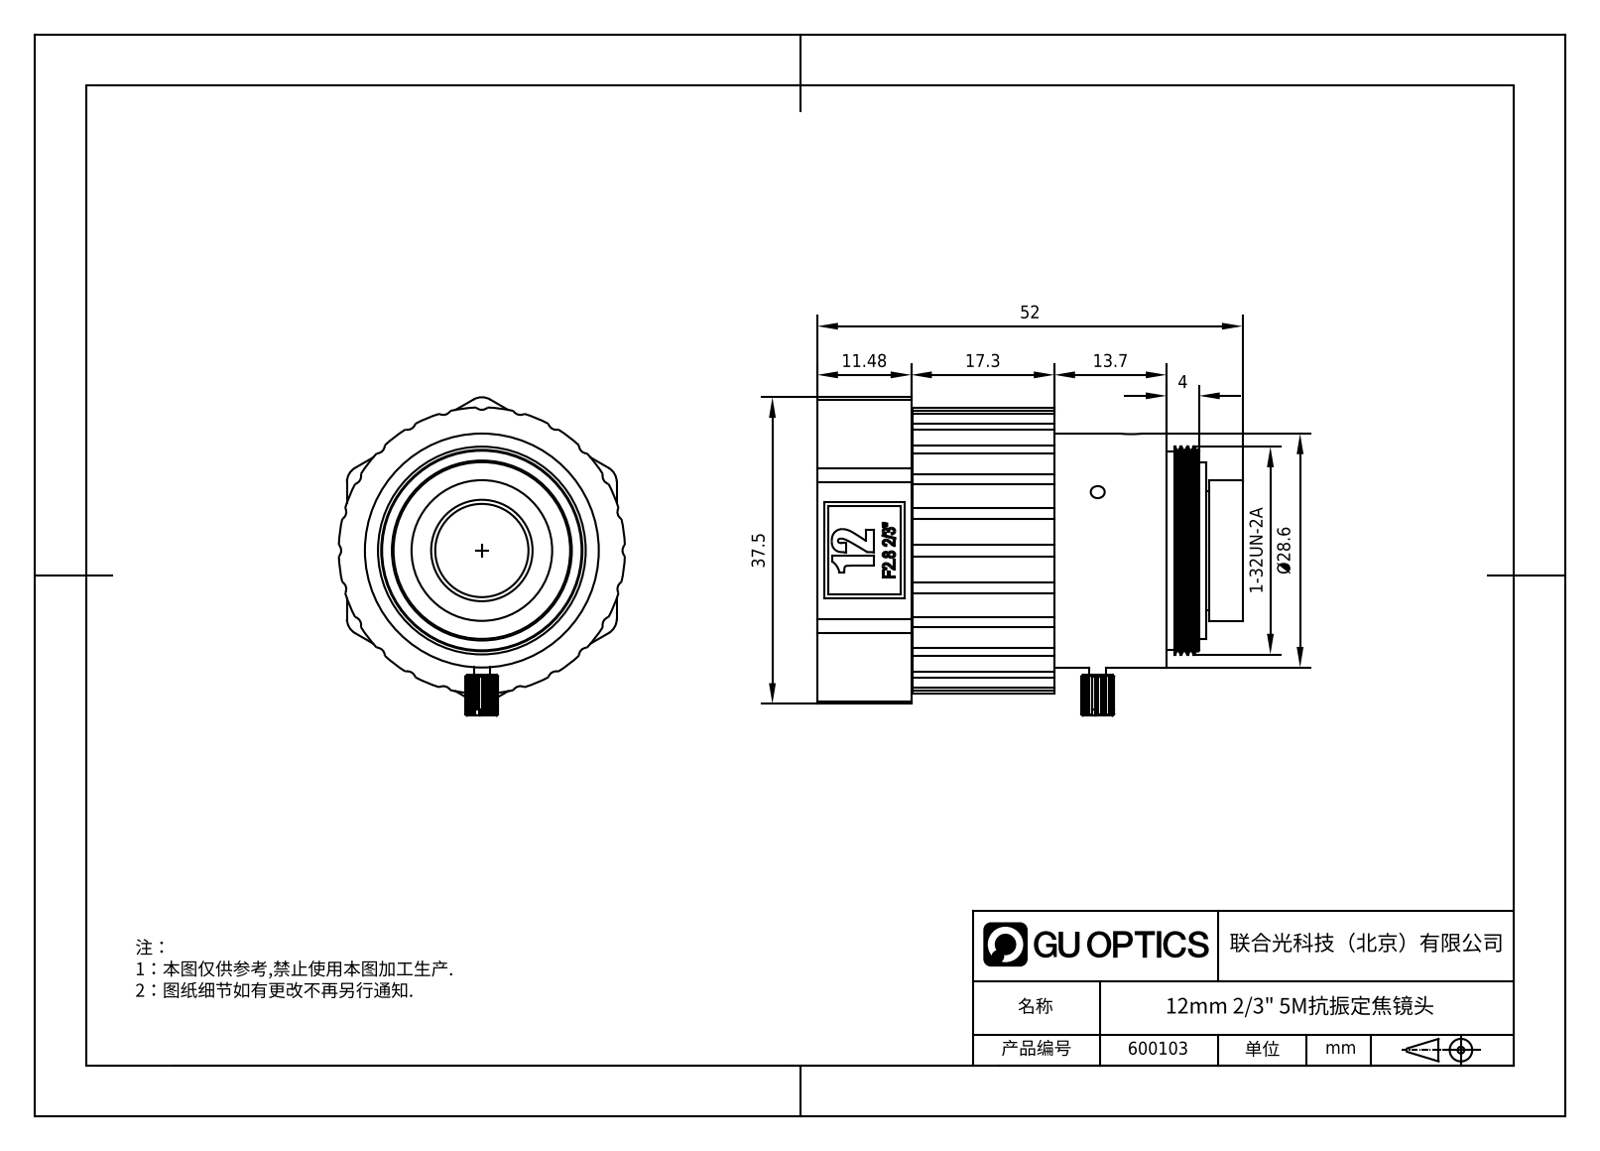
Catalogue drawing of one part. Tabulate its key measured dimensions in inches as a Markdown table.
| quantity | value |
| --- | --- |
| part name | 600103 |
| STEP written by | SolidWorks 2020 (CONFIG_CONTROL_DESIGN) |
| units | inches |
| bodies | 4 solids, 381 faces (186 planar, 120 cylindrical, 75 other) |
| overall size | 2.047 × 1.533 × 1.377 |
| volume | 2.127 in³ |
| surface area | 24.98 in² |
| round holes (diameter × count) | 0.067 × 3, 0.055 × 1, 0.11 × 1, 0.449 × 1, 0.614 × 1, 0.921 × 1, 1.039 × 1, 1.094 × 1, 1.102 × 1, 1.177 × 1, 1.181 × 1, 1.217 × 1 |
| round bosses / shafts (diameter × count) | 1.22 × 1, 1.173 × 1, 1.126 × 1, 1 × 1, 0.966 × 1, 0.961 × 1, 0.957 × 1, 0.866 × 1 |
| partial cylindrical surfaces (radius × count) | 0.039 × 24, 0.079 × 7, 0.689 × 1 |
| main face-to-face distances | 0.134, 0.556, 1.299, 0.484, 0.24, 0.861, 0.689, 0.452, 1.141, 1.04 |
| hole center spacings | 0.161 |
